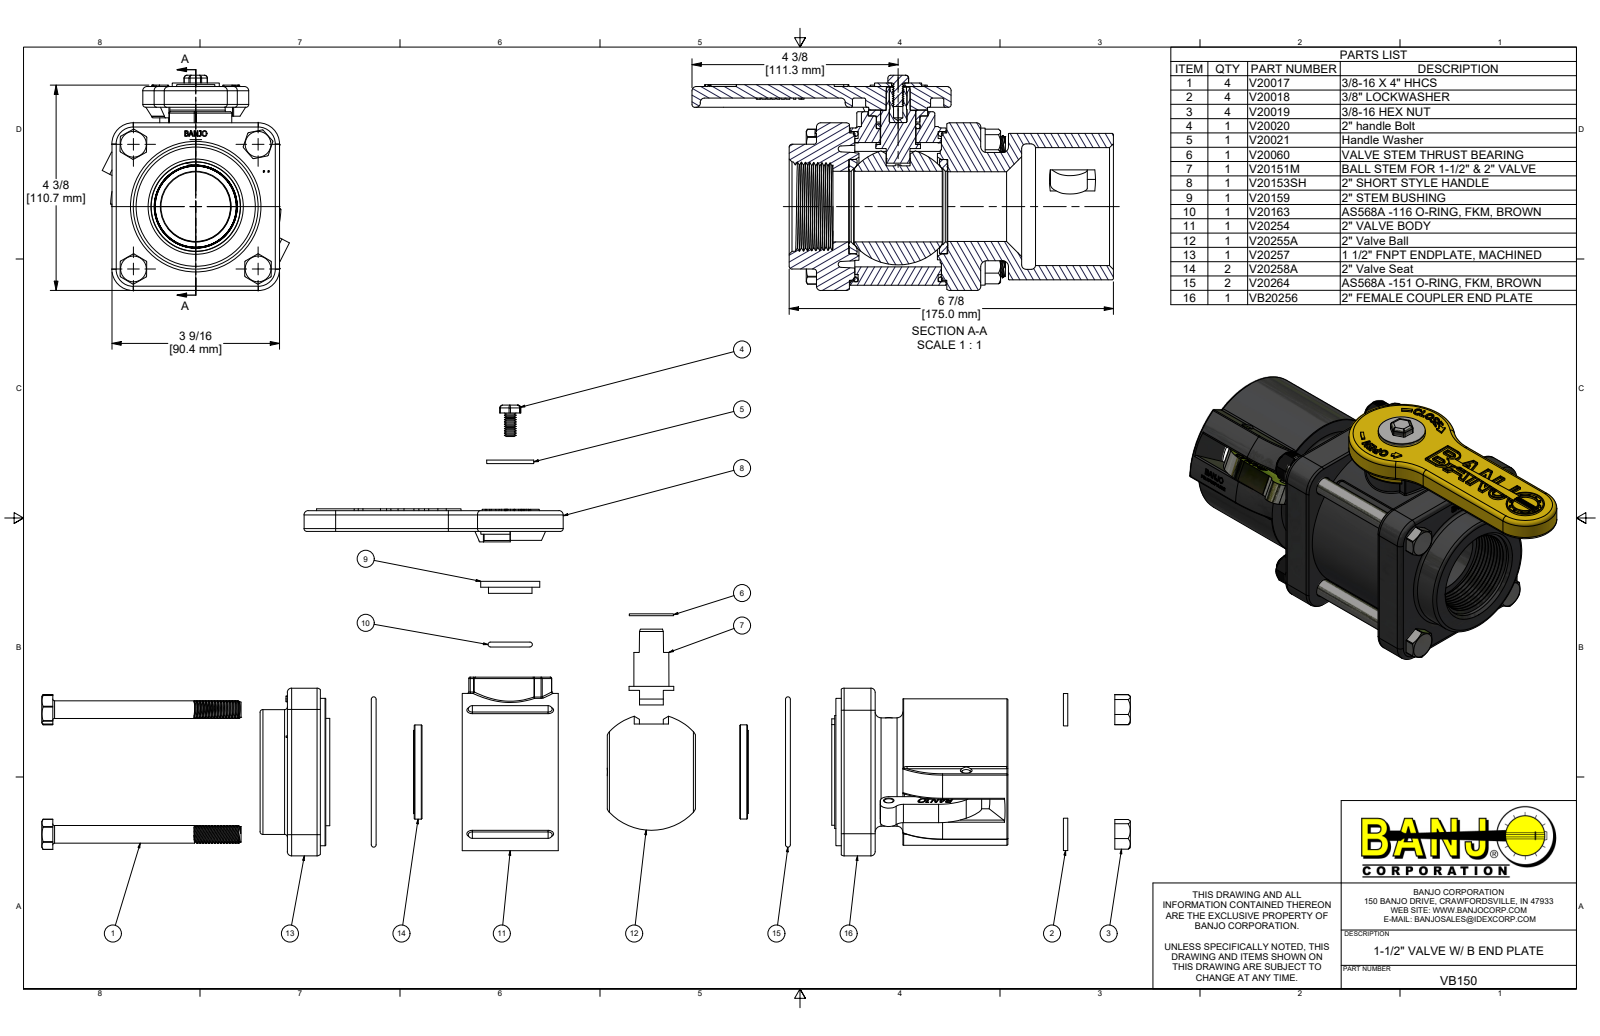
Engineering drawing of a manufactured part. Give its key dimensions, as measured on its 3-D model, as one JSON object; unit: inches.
{"part_name": "VB150; V20017; V20018; V20019 (+8 more)", "step_written_by": "Autodesk Inventor 2022 (AUTOMOTIVE_DESIGN)", "units": "inches", "bodies": {"solids": 33, "faces": 2780, "planar": 1211, "cylindrical": 548, "other": 1021}, "overall_size": [8.955, 4.571, 3.978], "volume_in3": 43.33, "surface_area_in2": 334.9, "round_holes": [[0.165, 10], [0.375, 5], [0.307, 4], [0.385, 4], [0.406, 4], [0.42, 4], [0.195, 2], [0.25, 2], [0.258, 2], [1.5, 2], [1.566, 2], [1.616, 2]], "round_bosses_or_shafts": [[0.324, 60], [0.687, 4], [0.375, 4], [2, 2], [1.766, 2], [0.26, 2], [0.249, 2], [3.13, 1]], "partial_cylinders_radius": [[0.03, 38], [0.09, 22], [0.06, 14], [0.125, 9], [0.162, 8], [0.18, 6], [0.015, 4], [0.094, 4]], "face_to_face_distances": [0.115, 1.955, 0.7, 3.56, 2.79, 3.49, 2.655, 0.835, 2.77, 0.72], "hole_center_spacings": [1.363, 1.872, 2.316, 2.632, 2.648, 2.813, 3.128, 0.705]}
